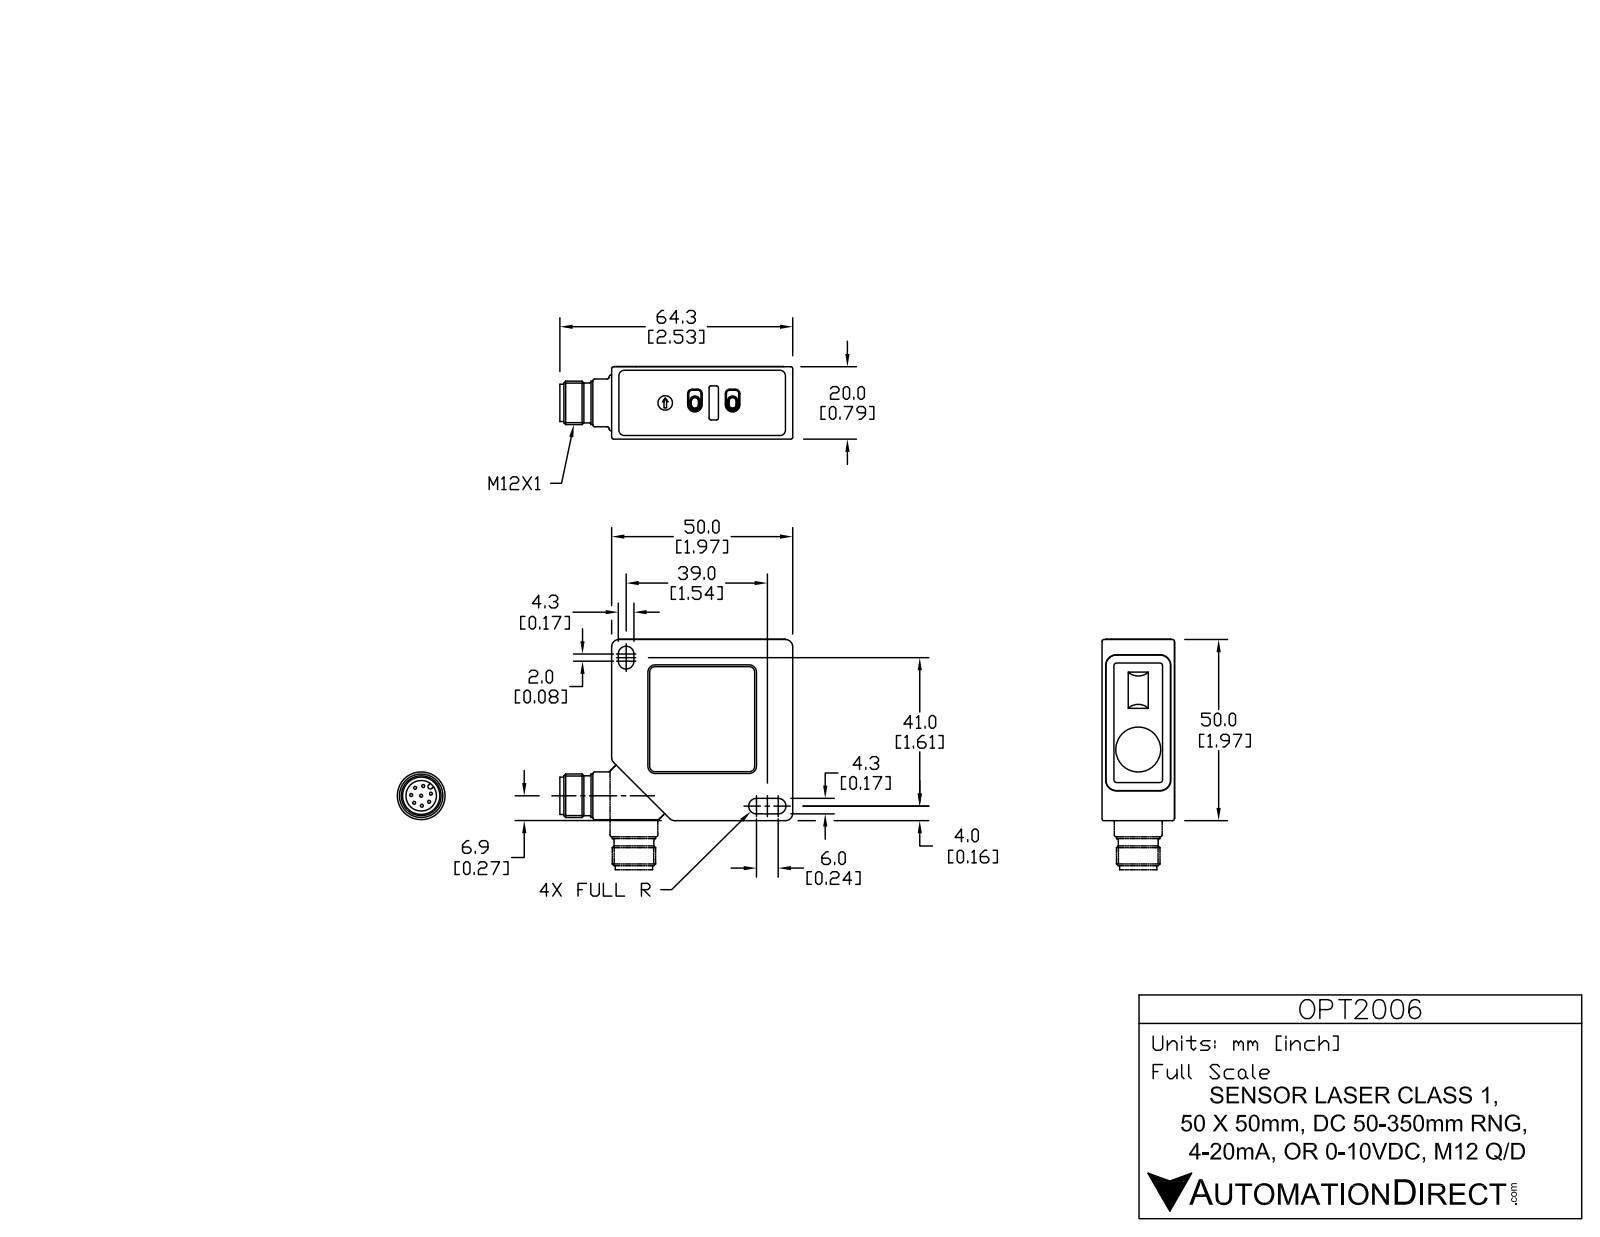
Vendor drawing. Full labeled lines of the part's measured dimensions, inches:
Part name (STEP PRODUCT): OPT2006
STEP written by: SolidWorks 2013 (AUTOMOTIVE_DESIGN)
Units: inches
Bodies: 15 solids, 301 faces (153 planar, 134 cylindrical, 14 other)
Overall size (bounding box): 2.537 × 1.972 × 0.787
Volume: 2.969 in³ · Surface area: 24.84 in²
Round holes (diameter × count): ⌀0.157 ×1, ⌀0.333 ×1
Round bosses / shafts (diameter × count): ⌀0.032 ×8, ⌀0.709 ×1, ⌀0.531 ×1, ⌀0.488 ×1, ⌀0.472 ×1, ⌀0.433 ×1, ⌀0.406 ×1
Partial cylindrical surfaces — rounded edges, fillets, slot ends (radius × count): R0.079 ×17, R0.008 ×10, R0.039 ×8, R0.083 ×5, R0.02 ×4, R0.047 ×4, R0.085 ×4, R0.114 ×4
Main face-to-face distances: 0.787, 0.78, 1.969, 1.972, 1.902, 0.063, 1.906, 0.21, 2.111, 2.115
